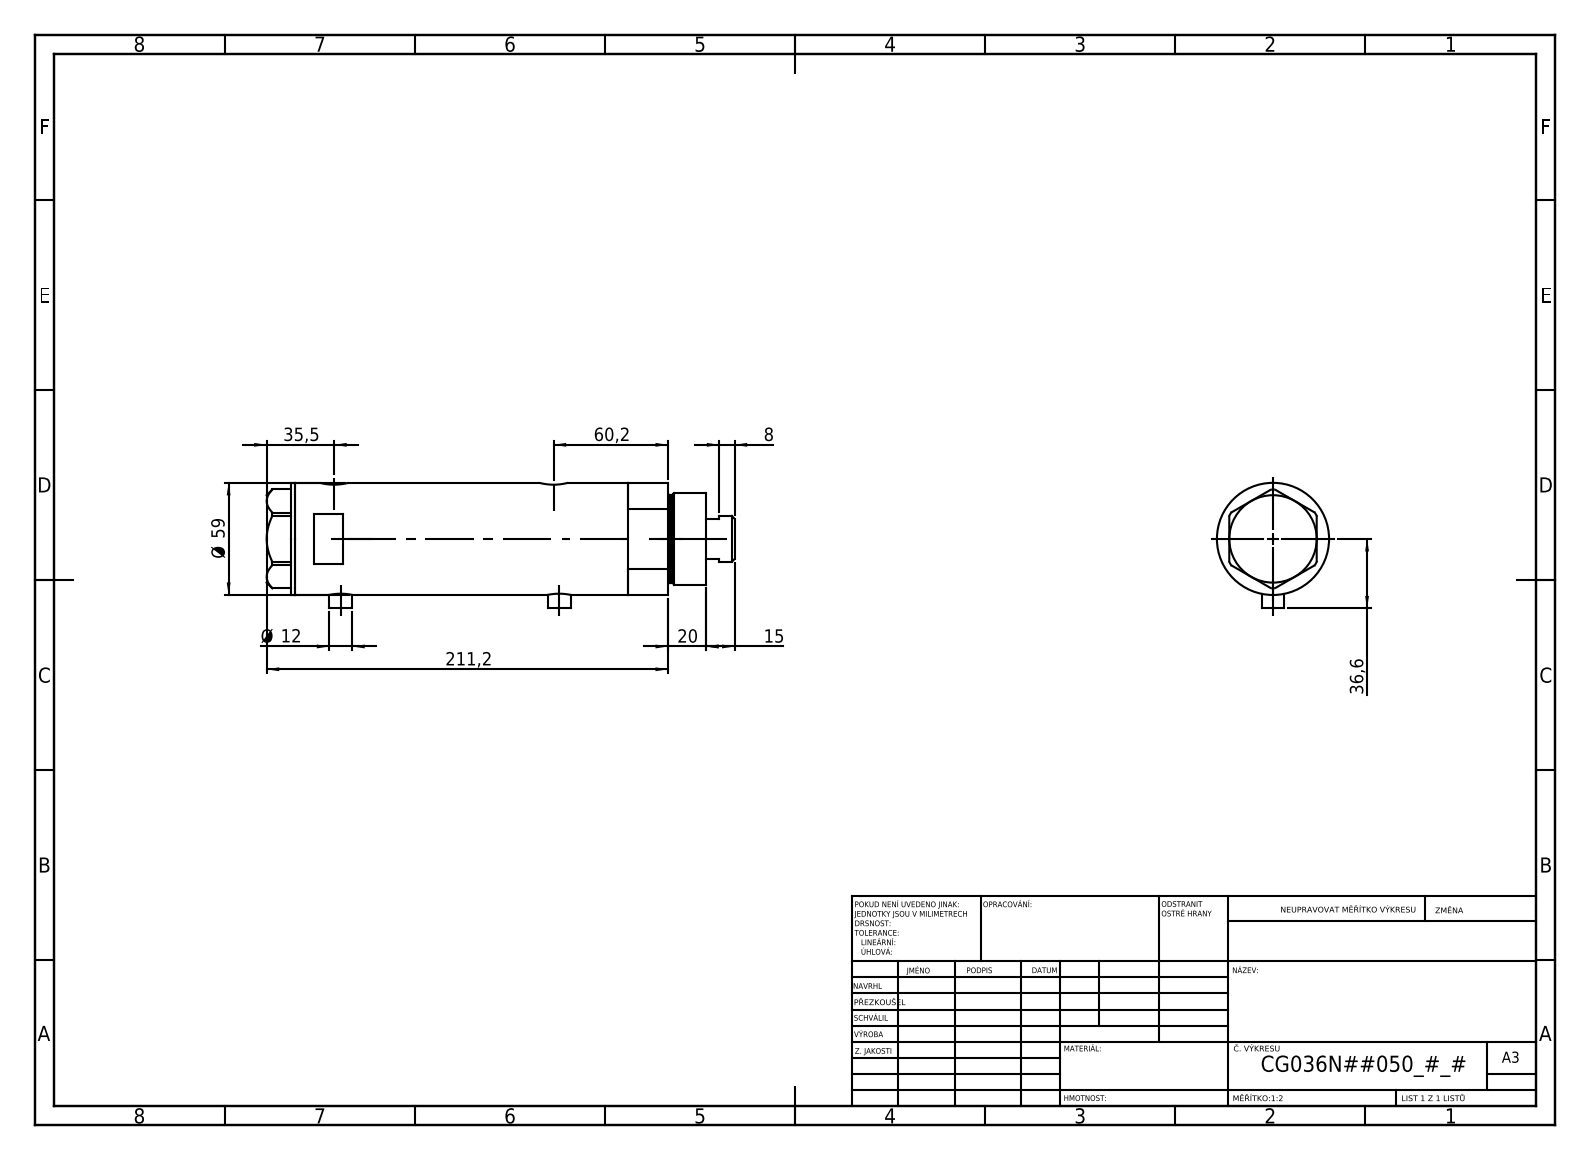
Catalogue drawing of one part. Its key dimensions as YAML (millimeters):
part_name: "V270CG_BACK; V270CG_FRONT; V270CG_VC; V270CG_MIDDLE"
step_written_by: "SolidWorks 2019 (CONFIG_CONTROL_DESIGN)"
units: millimeters
bodies: {solids: 4, faces: 120, planar: 51, cylindrical: 49, other: 20}
overall_size: [246.2, 66.1, 59]
volume: 574133
surface_area: 114379
round_holes:
  - {diameter: 9.73, count: 2}
  - {diameter: 12.5, count: 2}
  - {diameter: 15, count: 2}
  - {diameter: 8.5, count: 1}
  - {diameter: 25, count: 1}
  - {diameter: 26.5, count: 1}
  - {diameter: 36, count: 1}
  - {diameter: 40, count: 1}
  - {diameter: 52, count: 1}
round_bosses_or_shafts:
  - {diameter: 12, count: 2}
  - {diameter: 59, count: 1}
  - {diameter: 48, count: 1}
  - {diameter: 46, count: 1}
  - {diameter: 24, count: 1}
face_to_face_distances: [137.2, 23.5, 113.7, 15, 38.5, 152.2, 2, 231.2, 216.2, 50]
hole_center_spacings: [2.9, 3.5, 112, 114.9, 115.5, 118.4]
